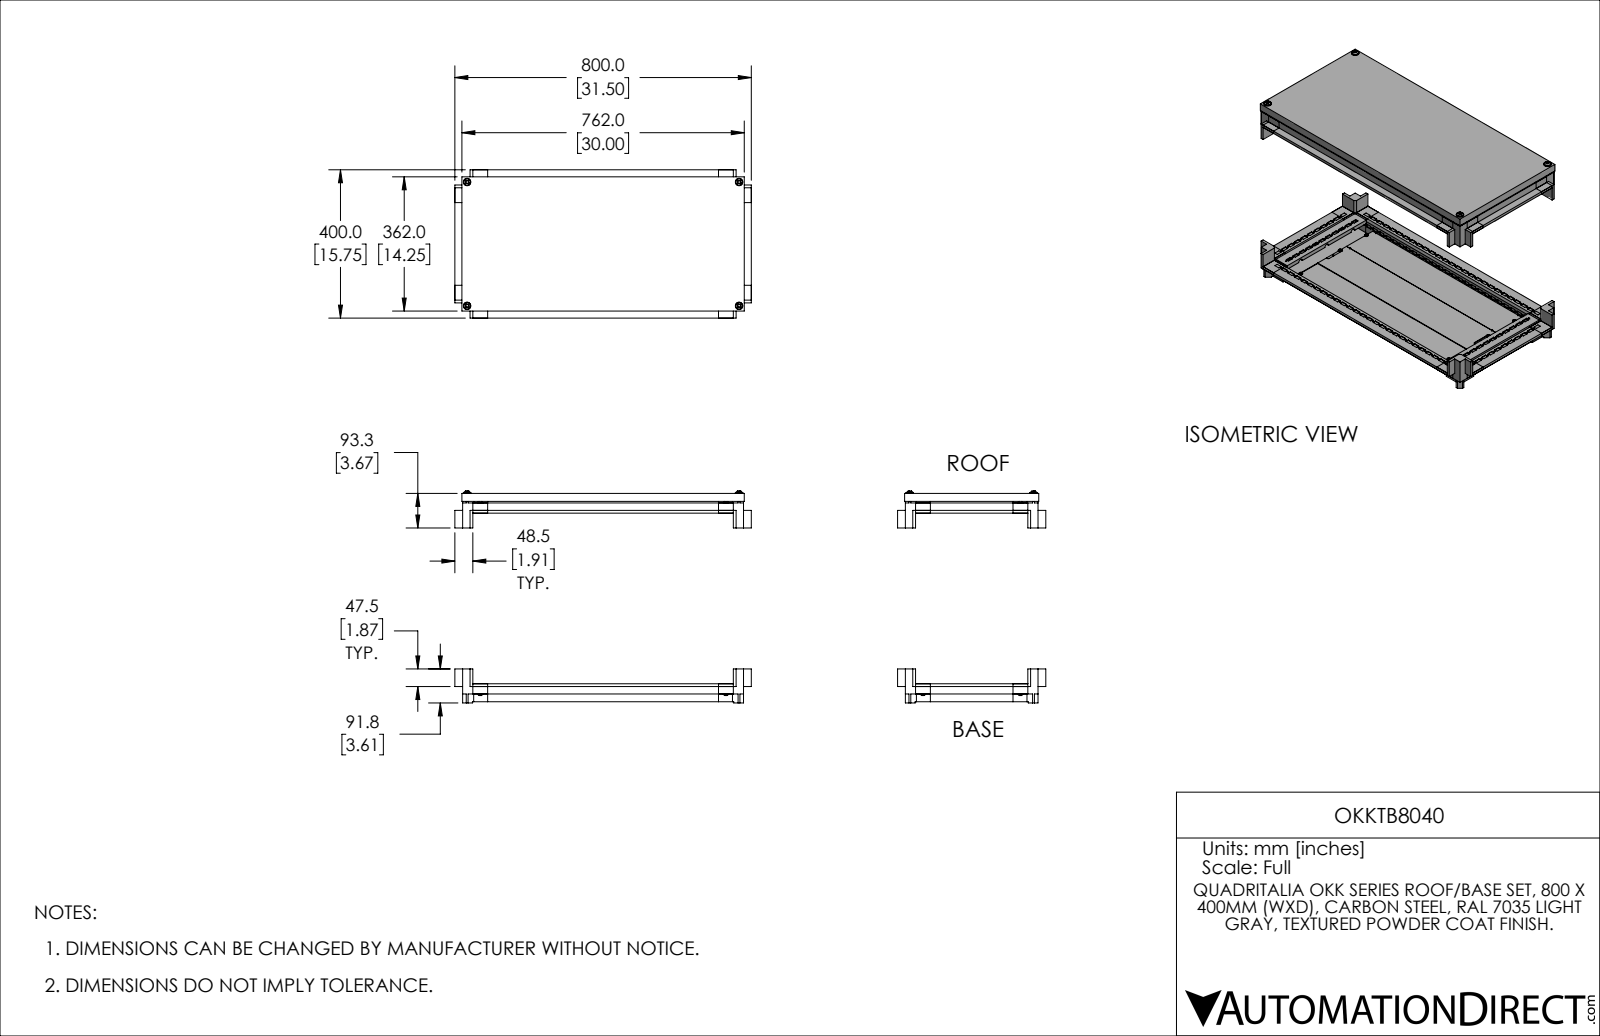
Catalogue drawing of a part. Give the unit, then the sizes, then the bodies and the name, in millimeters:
Units: millimetres
Overall size (bounding box): 800 × 571.4 × 400
Round holes (diameter × count): ⌀4.2 ×188, ⌀9 ×11, ⌀3.9 ×8, ⌀13.5 ×4, ⌀4.9 ×3, ⌀8.2 ×3
Round bosses / shafts (diameter × count): ⌀14 ×11, ⌀8 ×11, ⌀10 ×9, ⌀5 ×6, ⌀20 ×4, ⌀12 ×4, ⌀6 ×4, ⌀7 ×1
Partial cylindrical surfaces — rounded edges, fillets, slot ends (radius × count): R0.5 ×264, R1 ×24, R0.3 ×16, R4.5 ×12, R3.5 ×8, R5.5 ×6, R7 ×3, R0.8 ×2
Main face-to-face distances: 1.5, 538.4, 20, 539.9, 27.5, 7.5, 20.5, 2.5, 17.5, 25
Hole centre spacings: 25, 50, 75, 100, 125, 150, 175, 200
Volume: 6 691 000 mm³ · Surface area: 2 401 000 mm²
Bodies: 59 solids, 4079 faces (3098 planar, 822 cylindrical, 159 other)
Part name (STEP PRODUCT): OKKTB8040
STEP written by: SolidWorks 2021 (AUTOMOTIVE_DESIGN)
